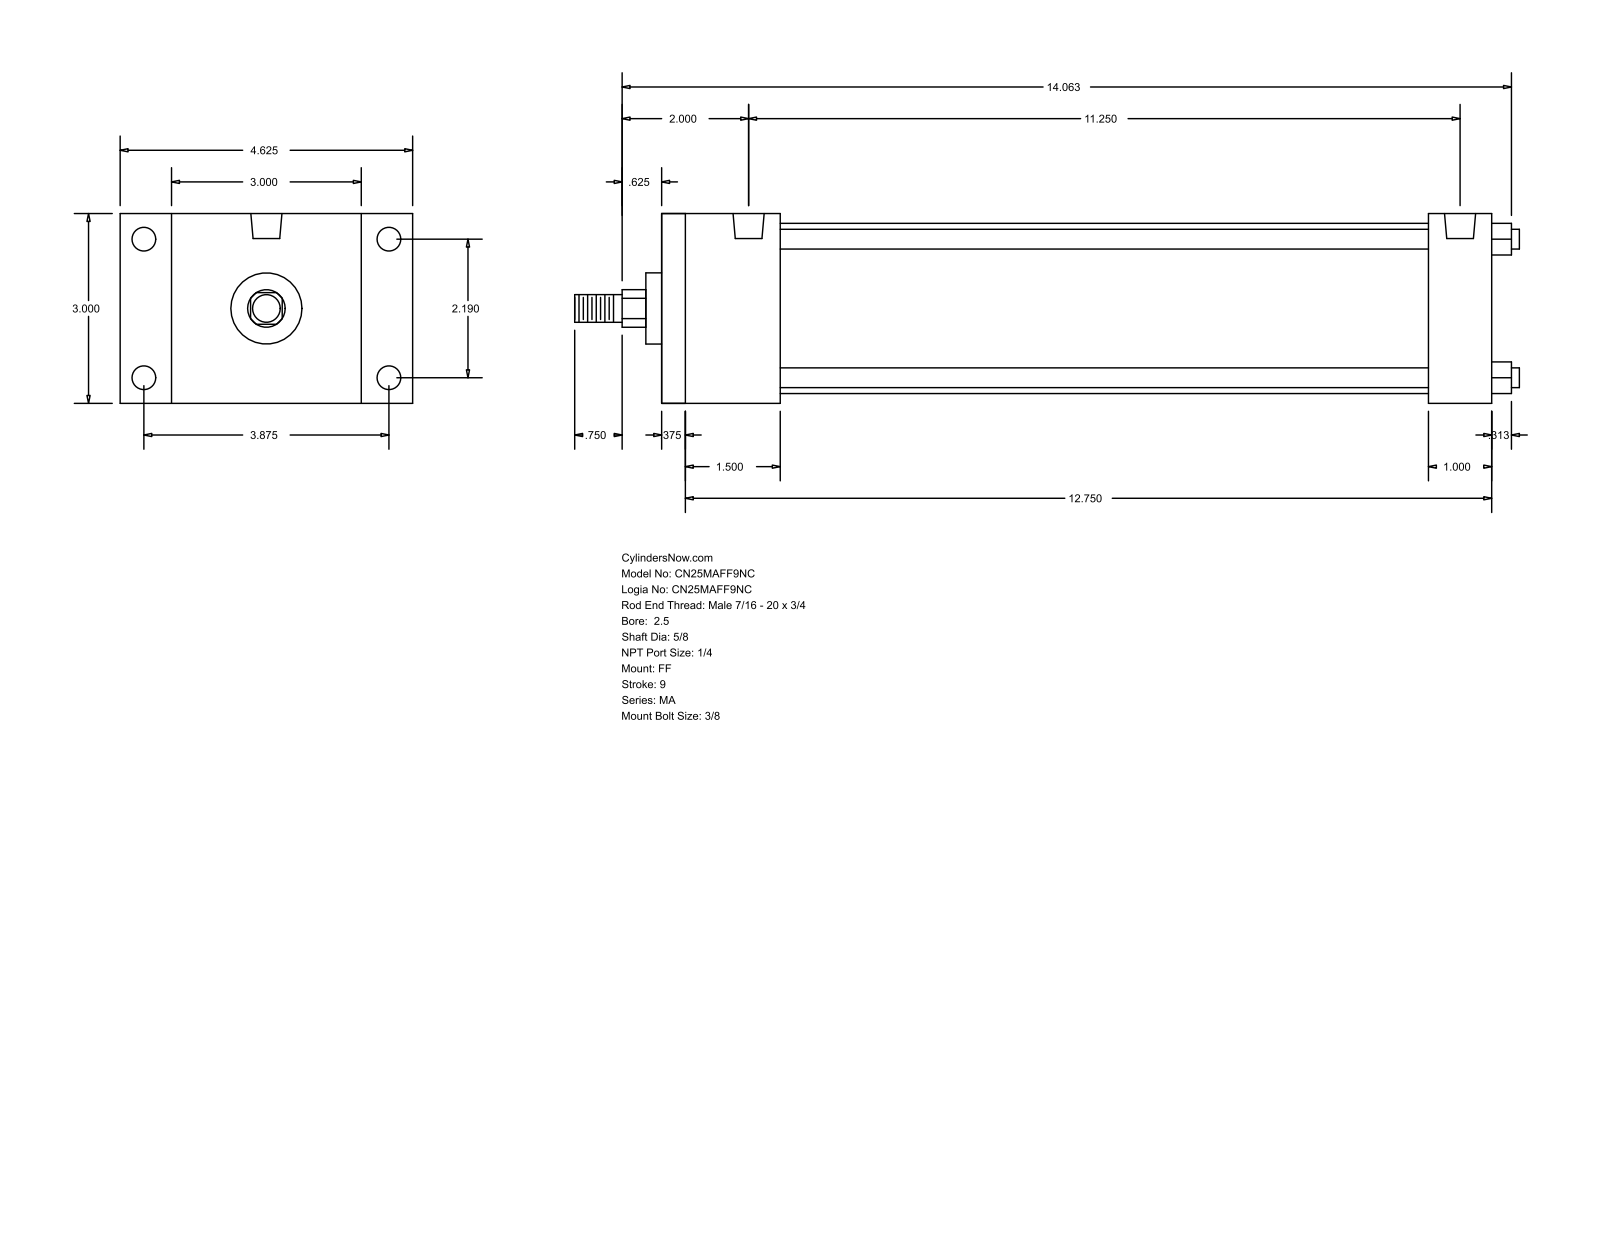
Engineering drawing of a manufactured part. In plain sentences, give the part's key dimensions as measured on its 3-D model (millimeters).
The part is named "MA_FF__0250_0.625". Its 3-D file was written by "GSSL Pune (CONFIG_CONTROL_DESIGN)". It is 0 solids with 92 faces: 64 planar, 28 cylindrical and 0 other. Overall it measures 379.41 by 117.47 by 76.2 millimeters. Round holes: 4 of diameter 7.94, 4 of diameter 9.53, 2 of diameter 12.49. Round bosses or shafts: 4 of diameter 7.94, 1 of diameter 68.33, 1 of diameter 28.57, 1 of diameter 15.88, 1 of diameter 11.11. Partial cylindrical surfaces (rounded edges, fillets, slot ends): 1 of radius 7.54. The main face-to-face distances are 76.2, 333.37, 323.85, 9.52, 25.4, 47.62, 307.97, 38.1, 298.45, 260.35. The hole center spacings are 55.62, 98.42, 113.05, 285.75.
